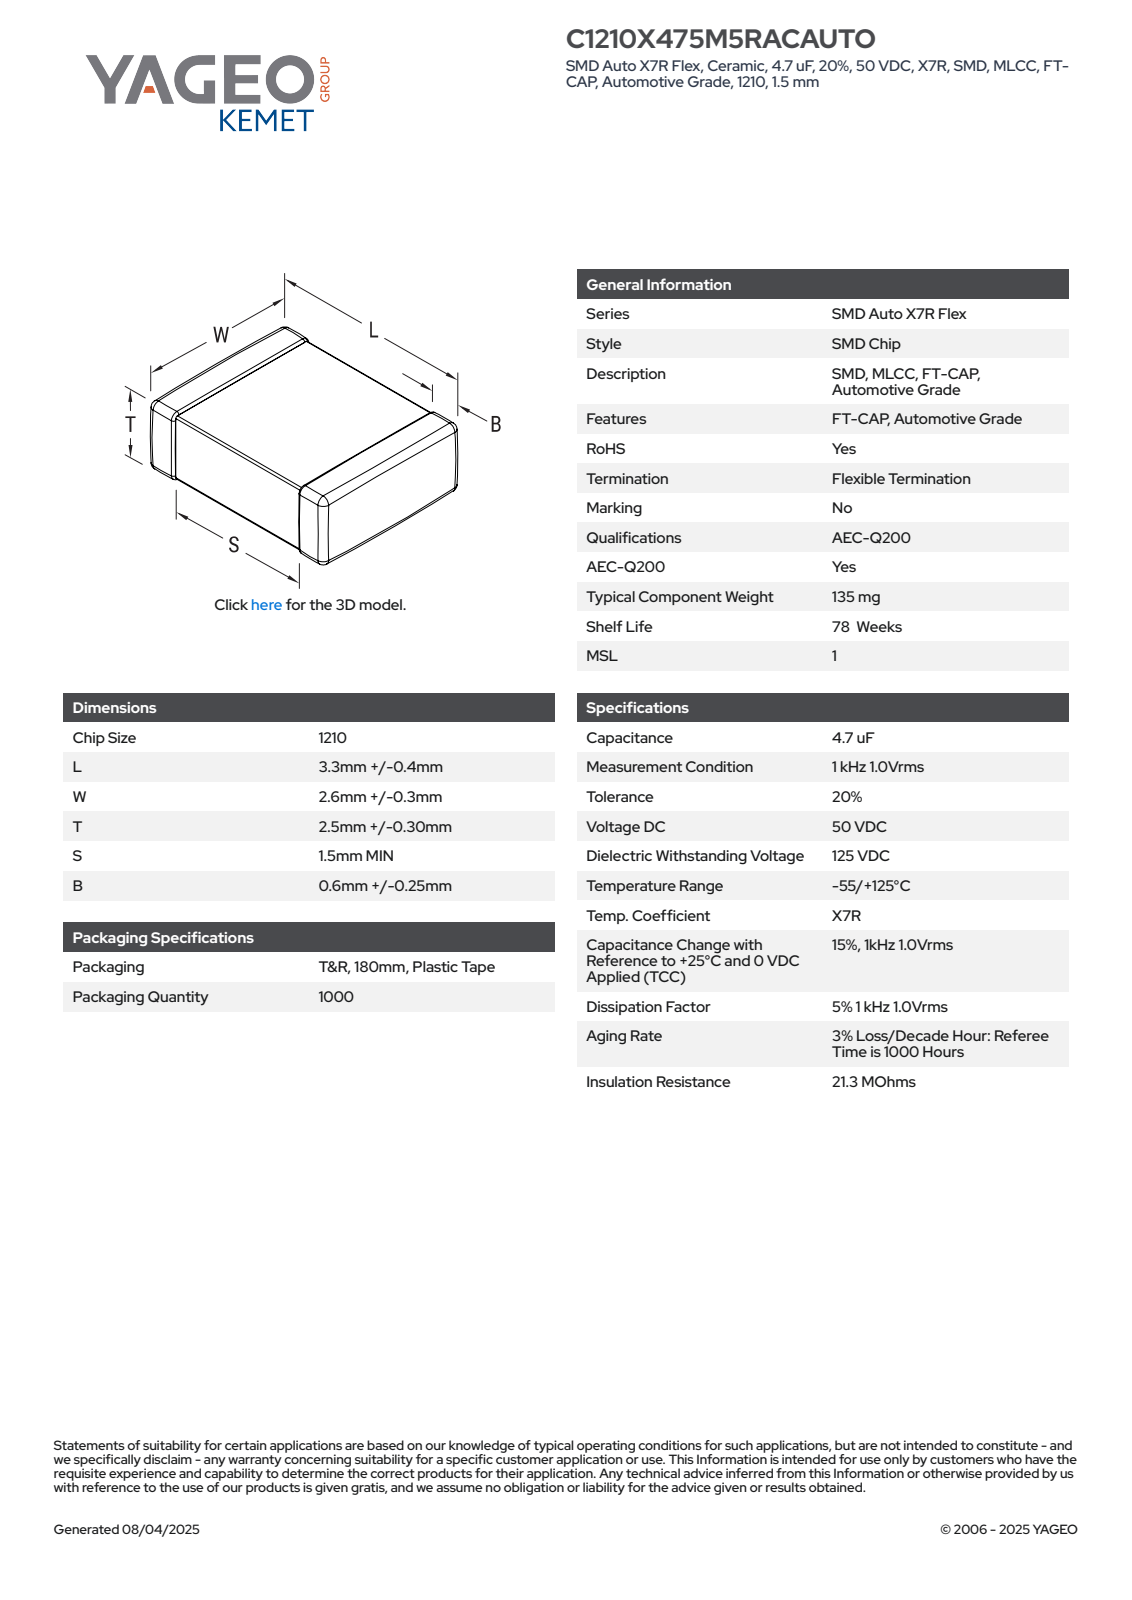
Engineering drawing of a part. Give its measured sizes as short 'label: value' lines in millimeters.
name: CCS_CCSTDNOS_1210_L3.7W2.9T2.8B0.85
written by: SolidWorks 2014 (AUTOMOTIVE_DESIGN)
unit: mm
bodies: 4 solids, 125 faces (71 planar, 38 cylindrical, 16 other)
size: 3.7 × 2.9 × 2.8
volume: 29 mm³; area: 58 mm²
face distances: 2.74, 2.84, 3.7, 2.68, 2.78, 2.8, 2.9, 1.4, 1.5, 1.34
